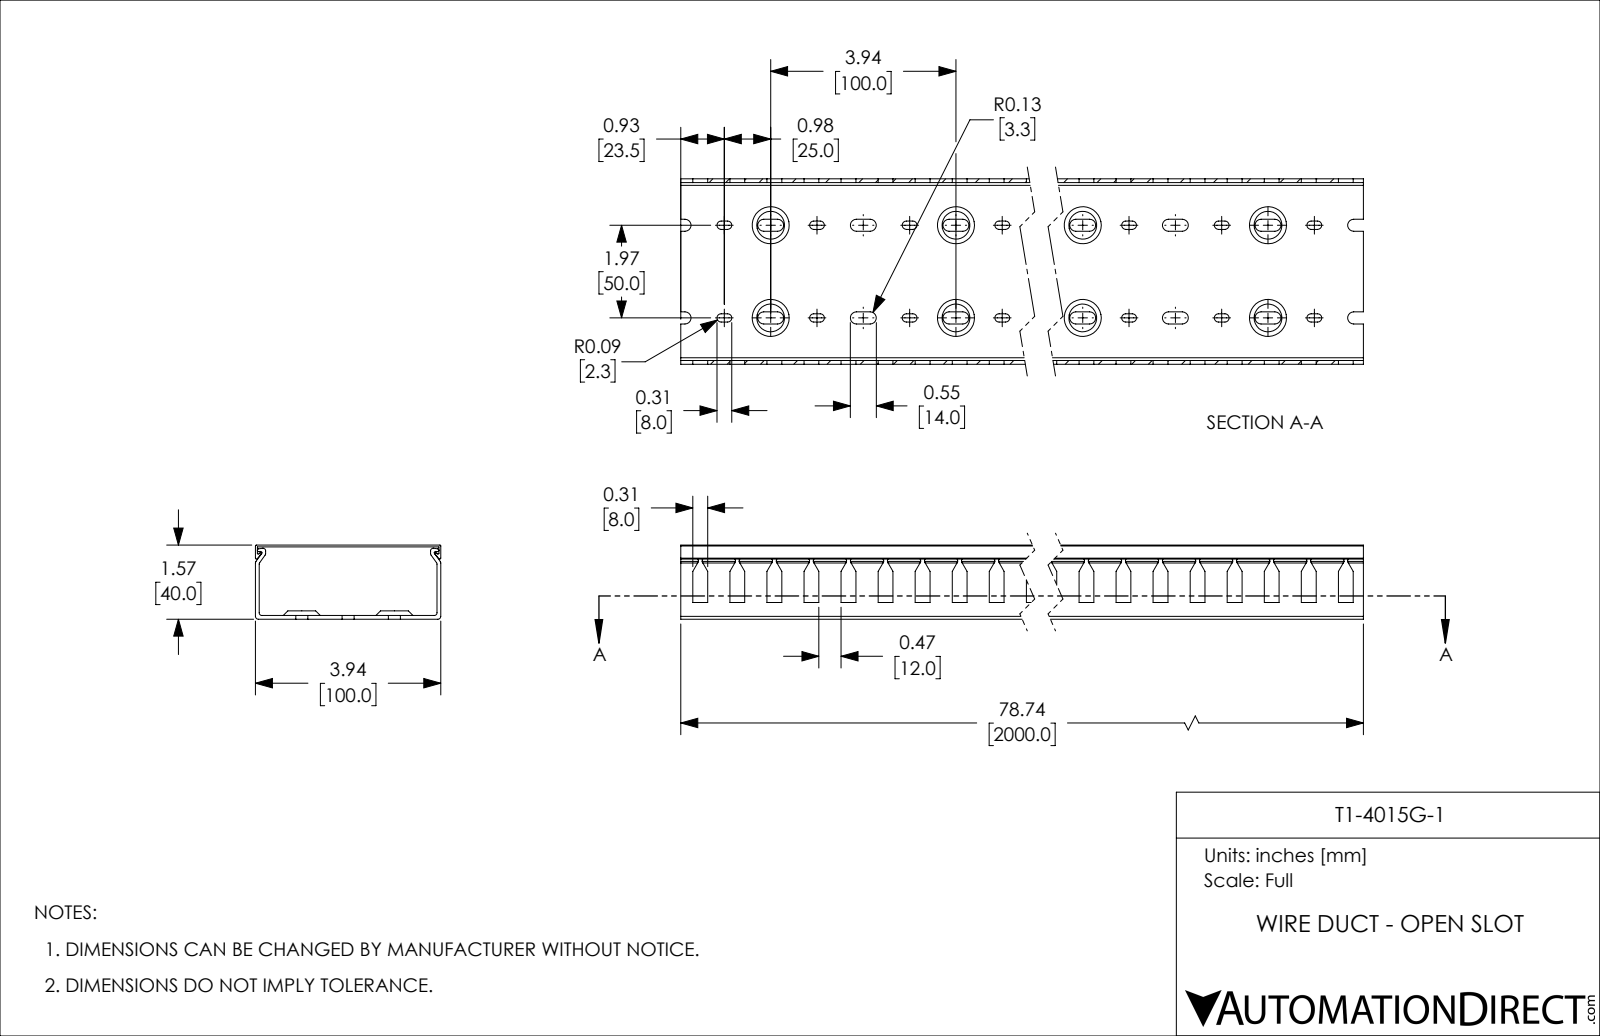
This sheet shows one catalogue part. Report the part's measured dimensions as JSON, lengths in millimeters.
{"part_name": "T1-4015G-1", "step_written_by": "SolidWorks 2021 (CONFIG_CONTROL_DESIGN)", "units": "millimeters", "bodies": {"solids": 2, "faces": 1573, "planar": 762, "cylindrical": 731, "other": 80}, "overall_size": [2000, 100, 40], "volume_mm3": 936759, "surface_area_mm2": 1173000, "partial_cylinders_radius": [[3.25, 200], [2.25, 160], [1.5, 12], [0.5, 8], [0.75, 6]], "face_to_face_distances": [2, 1, 40, 39, 37, 38, 98, 100, 96, 99]}
